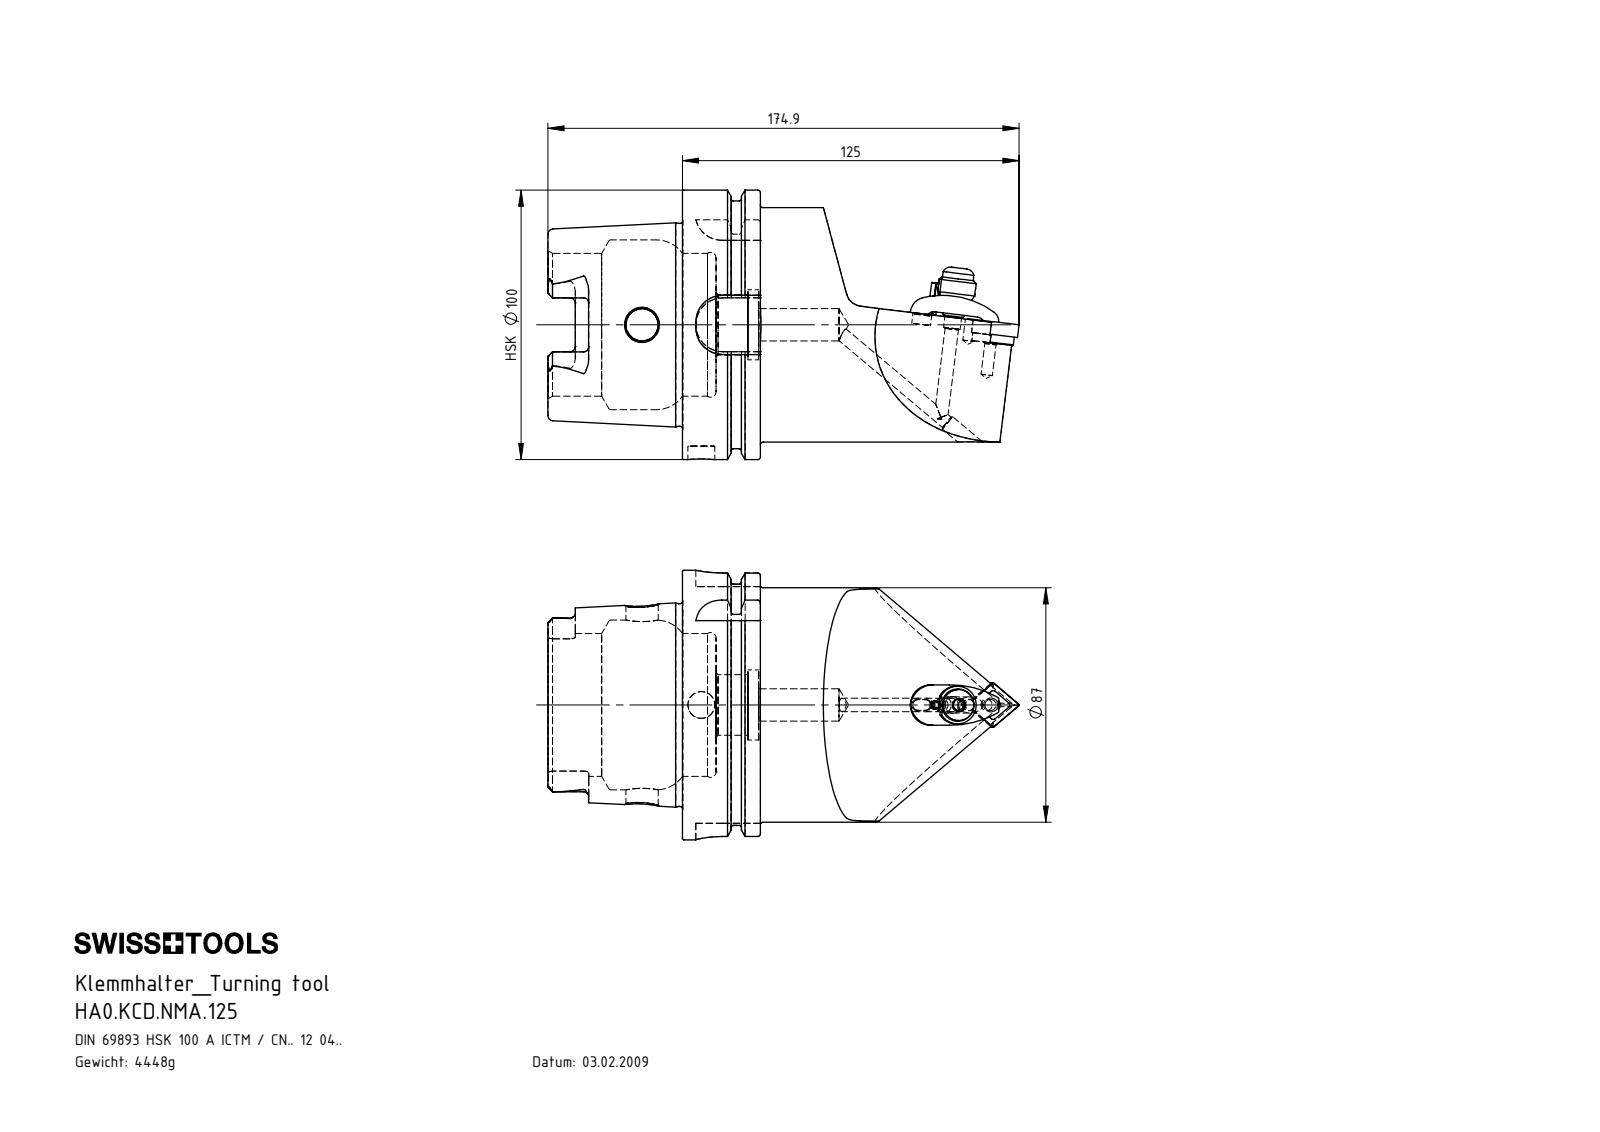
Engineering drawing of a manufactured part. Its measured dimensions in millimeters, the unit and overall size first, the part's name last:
Units: millimetres
Overall size (bounding box): 174.9 × 100 × 100
Round holes (diameter × count): ⌀2 ×3, ⌀5 ×3, ⌀4.2 ×2, ⌀7 ×2, ⌀12 ×2, ⌀2.4 ×1, ⌀3 ×1, ⌀5.16 ×1, ⌀6 ×1, ⌀6.2 ×1, ⌀6.55 ×1, ⌀8.5 ×1
Round bosses / shafts (diameter × count): ⌀6 ×2, ⌀3 ×2, ⌀100 ×1, ⌀91.95 ×1, ⌀87 ×1, ⌀75.26 ×1, ⌀14 ×1, ⌀11.5 ×1
Partial cylindrical surfaces — rounded edges, fillets, slot ends (radius × count): R0.39 ×6, R0.69 ×6, R1.9 ×6, R0.4 ×4, R1 ×4, R10 ×4, R1.5 ×3, R2 ×2
Main face-to-face distances: 12.45, 28.95, 16.5, 49.9, 62.35, 78.85, 87.8, 78.2, 28.3, 15.85
Hole centre spacings: 7.99, 8, 8.19, 14.67, 22.93, 22.99, 23.07, 6.48
Volume: 565 764 mm³ · Surface area: 74 045 mm²
Bodies: 11 solids, 460 faces (120 planar, 151 cylindrical, 189 other)
Part name (STEP PRODUCT): WCC-ER5.102.005_A; WCC-ER5.102.012_B; WCC-ER3.102.024_C; CNMG120404 (+7 more)
STEP written by: SolidWorks 2017 (AUTOMOTIVE_DESIGN)
